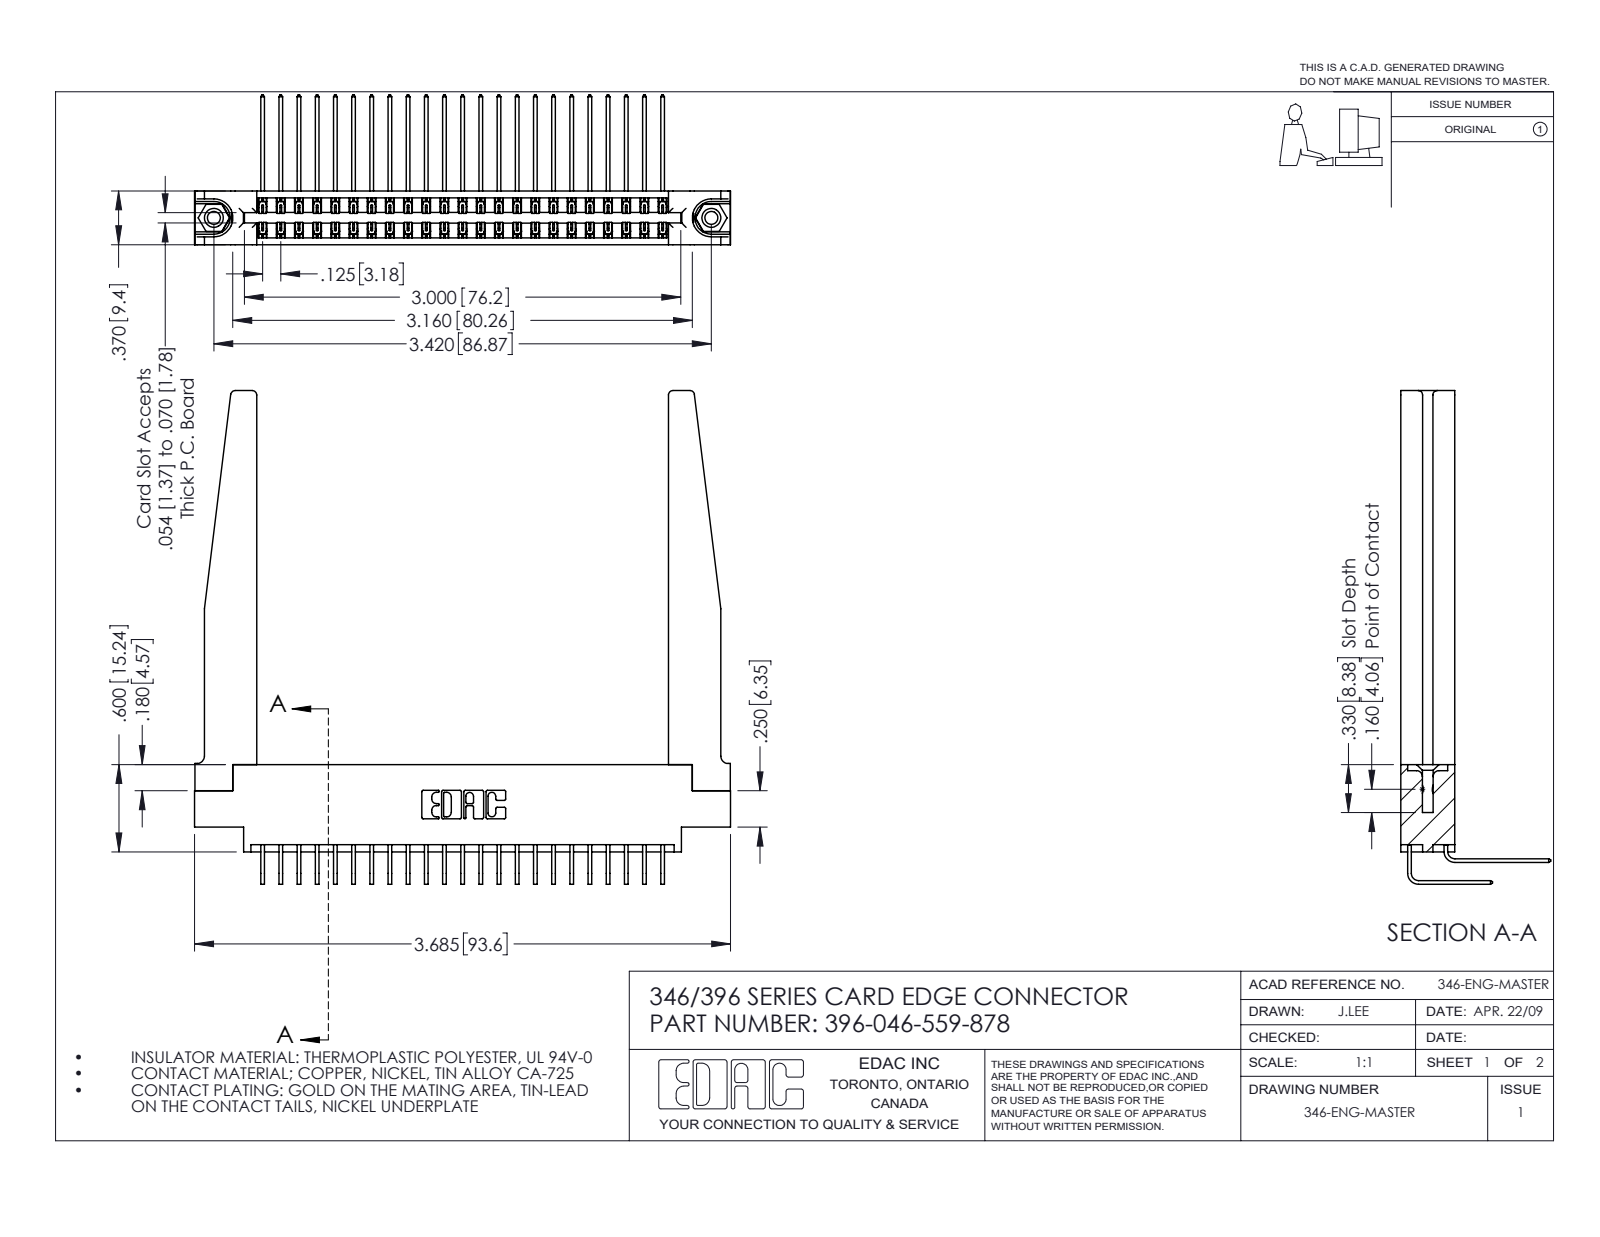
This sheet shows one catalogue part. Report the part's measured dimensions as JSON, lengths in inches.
{"part_name": "346-220-078_345-220-078; 346 Part_0.170 Offset - 0.156 Dia-TH; 345-292-001_559 Tail - 2; 345-250-001_345-250-001-102 (+2 more)", "step_written_by": "SolidWorks 2016 (CONFIG_CONTROL_DESIGN)", "units": "inches", "bodies": {"solids": 51, "faces": 2844, "planar": 1924, "cylindrical": 868, "other": 52}, "overall_size": [3.685, 3.393, 1.03], "volume_in3": 0.976, "surface_area_in2": 31.29, "round_holes": [[0.089, 2], [0.125, 2], [0.156, 2], [0.064, 1]], "round_bosses_or_shafts": [[0.155, 2]], "partial_cylinders_radius": [[0.006, 69], [0.01, 22], [0.03, 8], [0.007, 6], [0.031, 6], [0.05, 4], [0.026, 3], [0.014, 2]], "face_to_face_distances": [0.37, 0.048, 0.072, 0.322, 0.025, 0.148, 0.15, 0.25, 0.298, 0.275], "hole_center_spacings": [0.246, 3.212, 3.42]}
